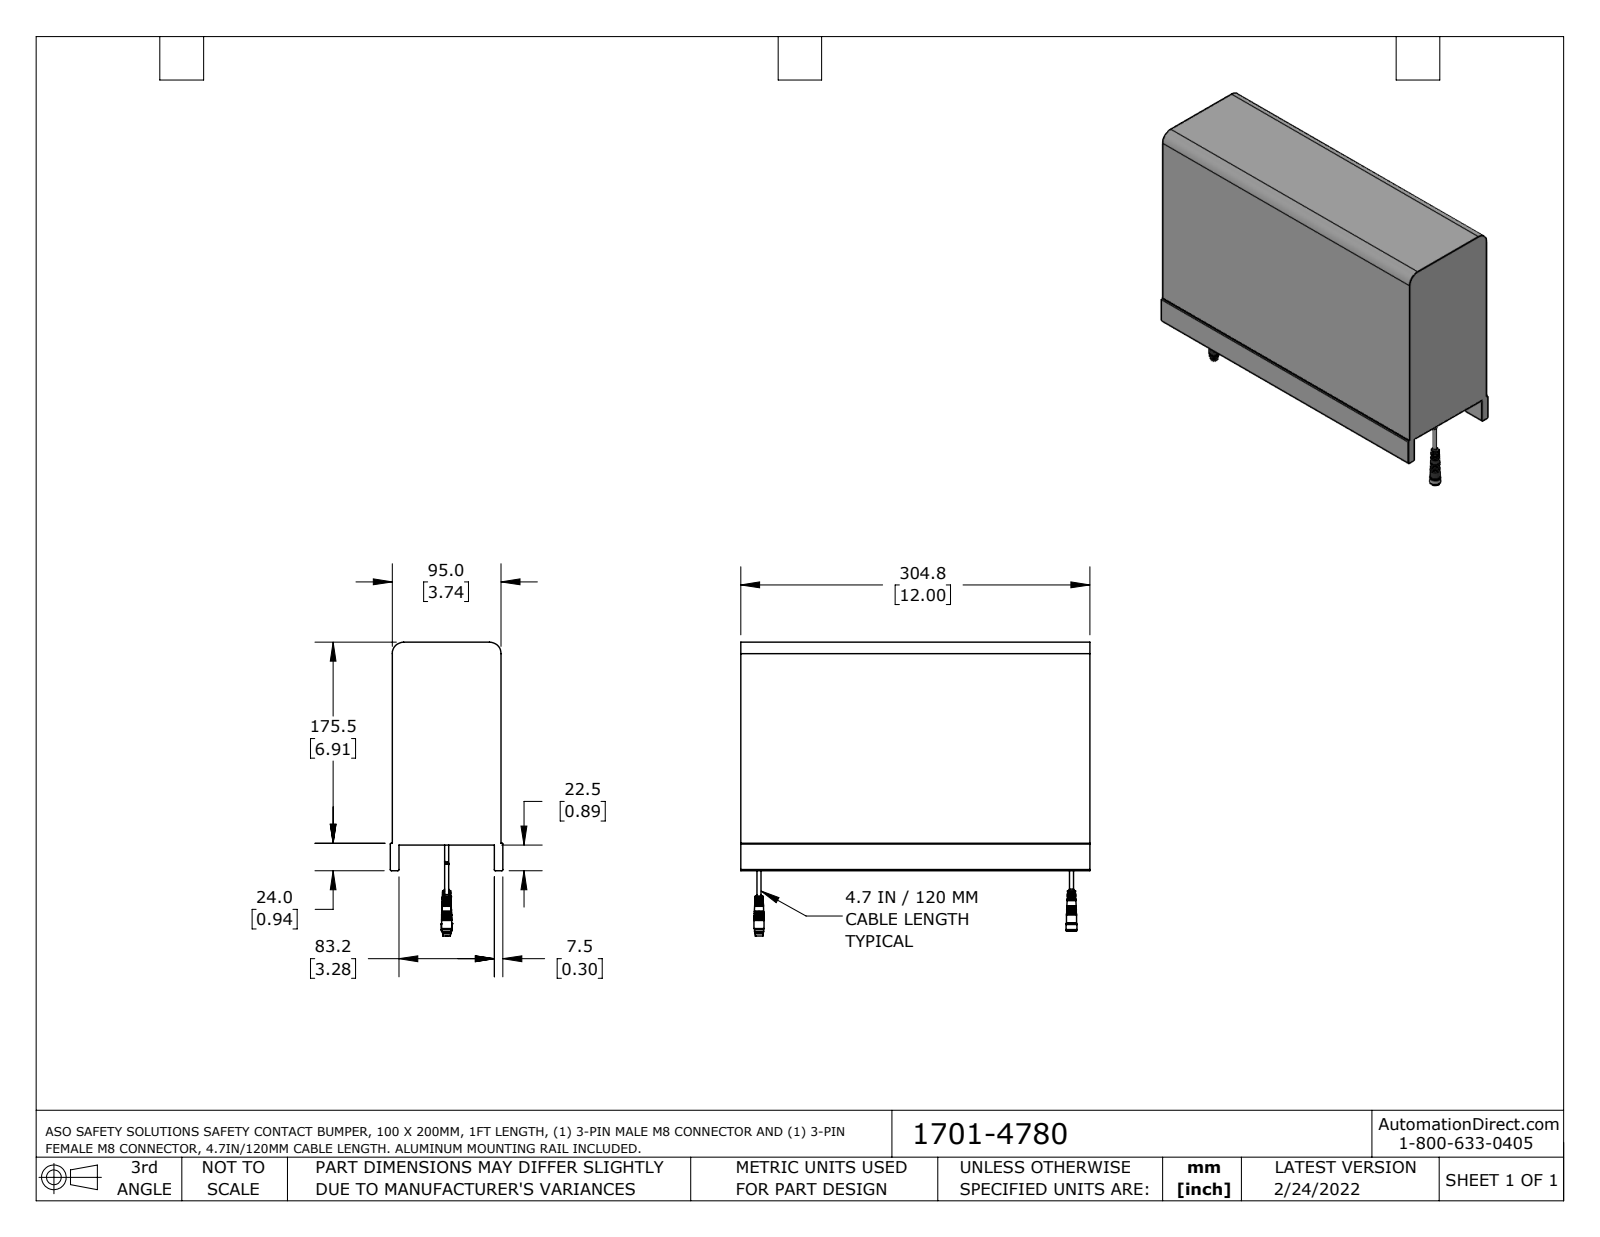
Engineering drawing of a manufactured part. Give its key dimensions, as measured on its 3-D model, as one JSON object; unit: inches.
{"part_name": "1701-4780_Default", "step_written_by": "SolidWorks 2021 (CONFIG_CONTROL_DESIGN)", "units": "inches", "bodies": {"solids": 24, "faces": 447, "planar": 175, "cylindrical": 154, "other": 118}, "overall_size": [12, 10.096, 3.868], "volume_in3": 318.6, "surface_area_in2": 361.1, "round_holes": [[0.047, 4], [0.033, 3], [0.063, 3], [0.134, 2], [0.228, 1], [0.232, 1], [0.272, 1], [0.283, 1]], "round_bosses_or_shafts": [[0.047, 8], [0.039, 6], [0.02, 4], [0.346, 2], [0.224, 2], [0.138, 2], [0.378, 1], [0.354, 1]], "partial_cylinders_radius": [[0.039, 4], [0.03, 2], [0.394, 2]], "face_to_face_distances": [3.74, 6.969, 12, 0.064, 3.804, 0.295, 3.572, 0.231, 3.509, 3.868], "hole_center_spacings": [0.028, 10.74, 0.069, 10.671, 10.713, 10.768, 10.809, 0.041]}
